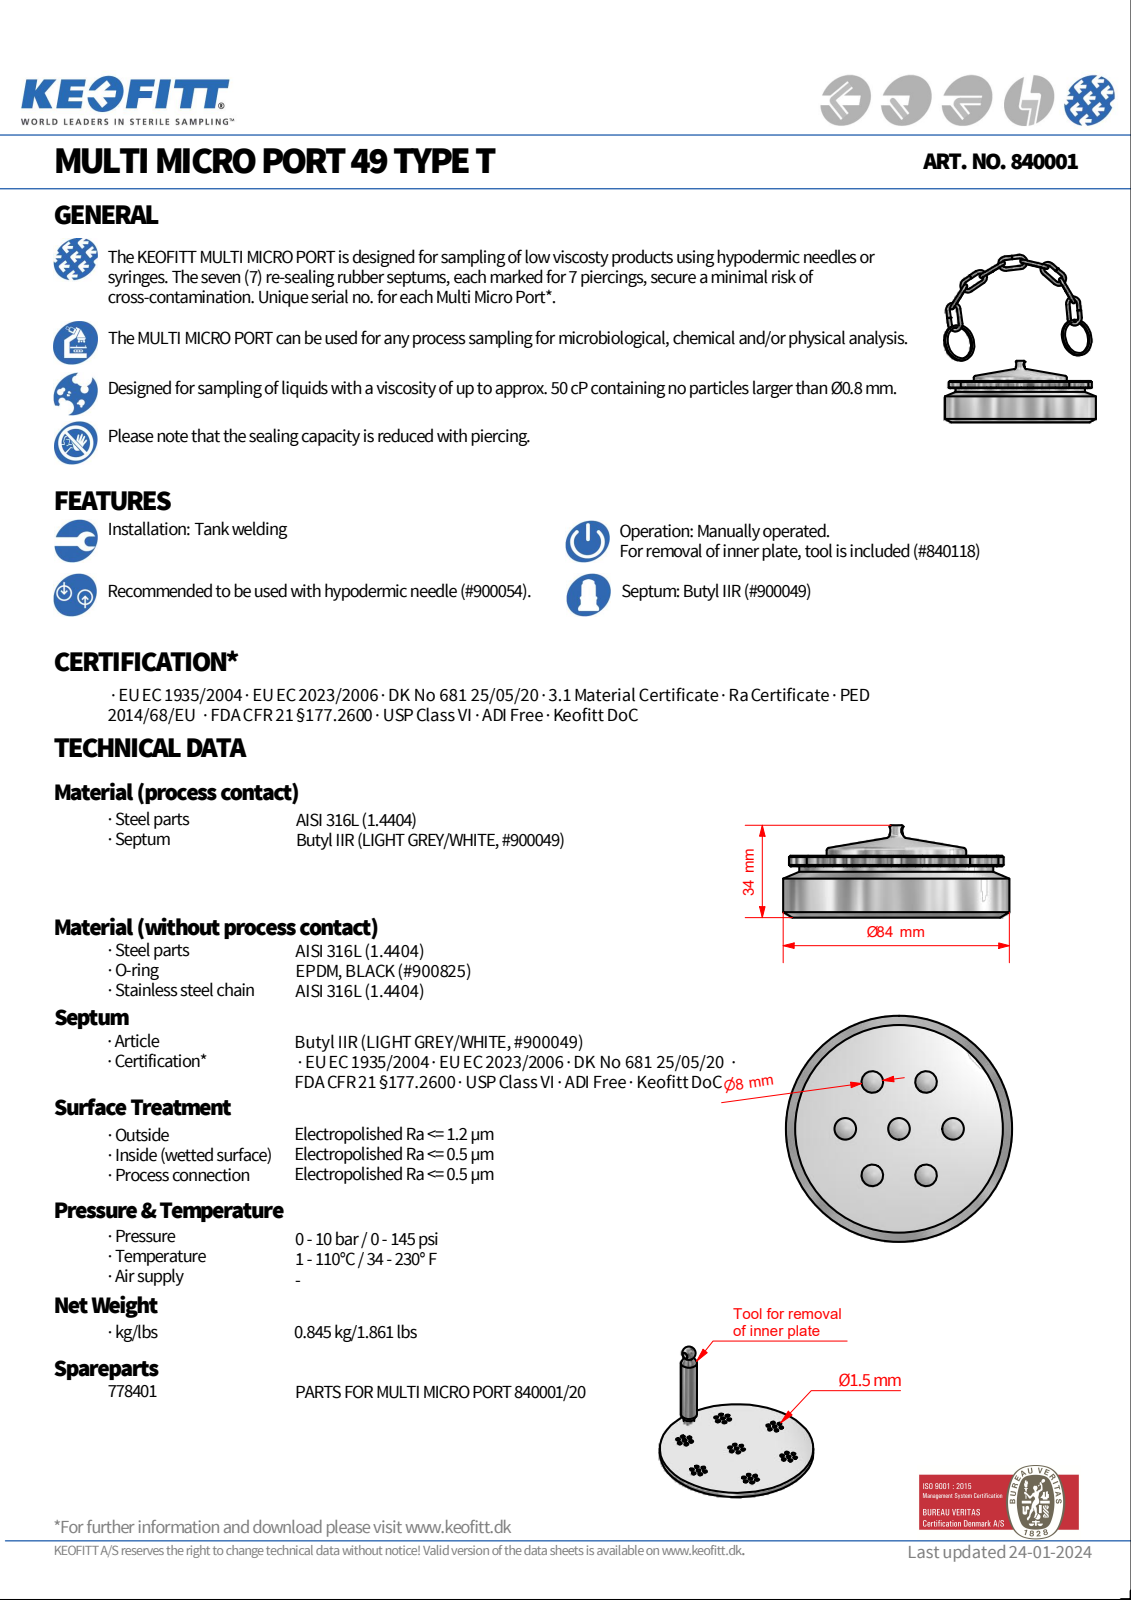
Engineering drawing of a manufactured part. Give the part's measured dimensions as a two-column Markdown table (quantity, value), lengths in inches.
| quantity | value |
| --- | --- |
| part name | 840001 |
| STEP written by | Autodesk Inventor 2017 (AUTOMOTIVE_DESIGN) |
| units | inches |
| bodies | 1 solid, 542 faces (283 planar, 66 cylindrical, 193 other) |
| overall size | 3.307 × 3.307 × 1.406 |
| volume | 7.69 in³ |
| surface area | 34.42 in² |
| round holes (diameter × count) | 0.315 × 7, 0.118 × 2, 0.157 × 2, 0.059 × 1, 1.724 × 1, 2.047 × 1 |
| round bosses / shafts (diameter × count) | 3.307 × 1, 2.835 × 1, 2.039 × 1, 0.197 × 1 |
| partial cylindrical surfaces (radius × count) | 0.157 × 24, 0.295 × 12, 1.575 × 1 |
| main face-to-face distances | 0.906, 0.079, 0.827, 0.913, 0.086, 0.748, 0.157, 0.165, 0.039, 0.709 |
| hole center spacings | 0.787, 1.364, 1.575, 0.57, 1.055, 1.274, 1.339, 1.789 |
